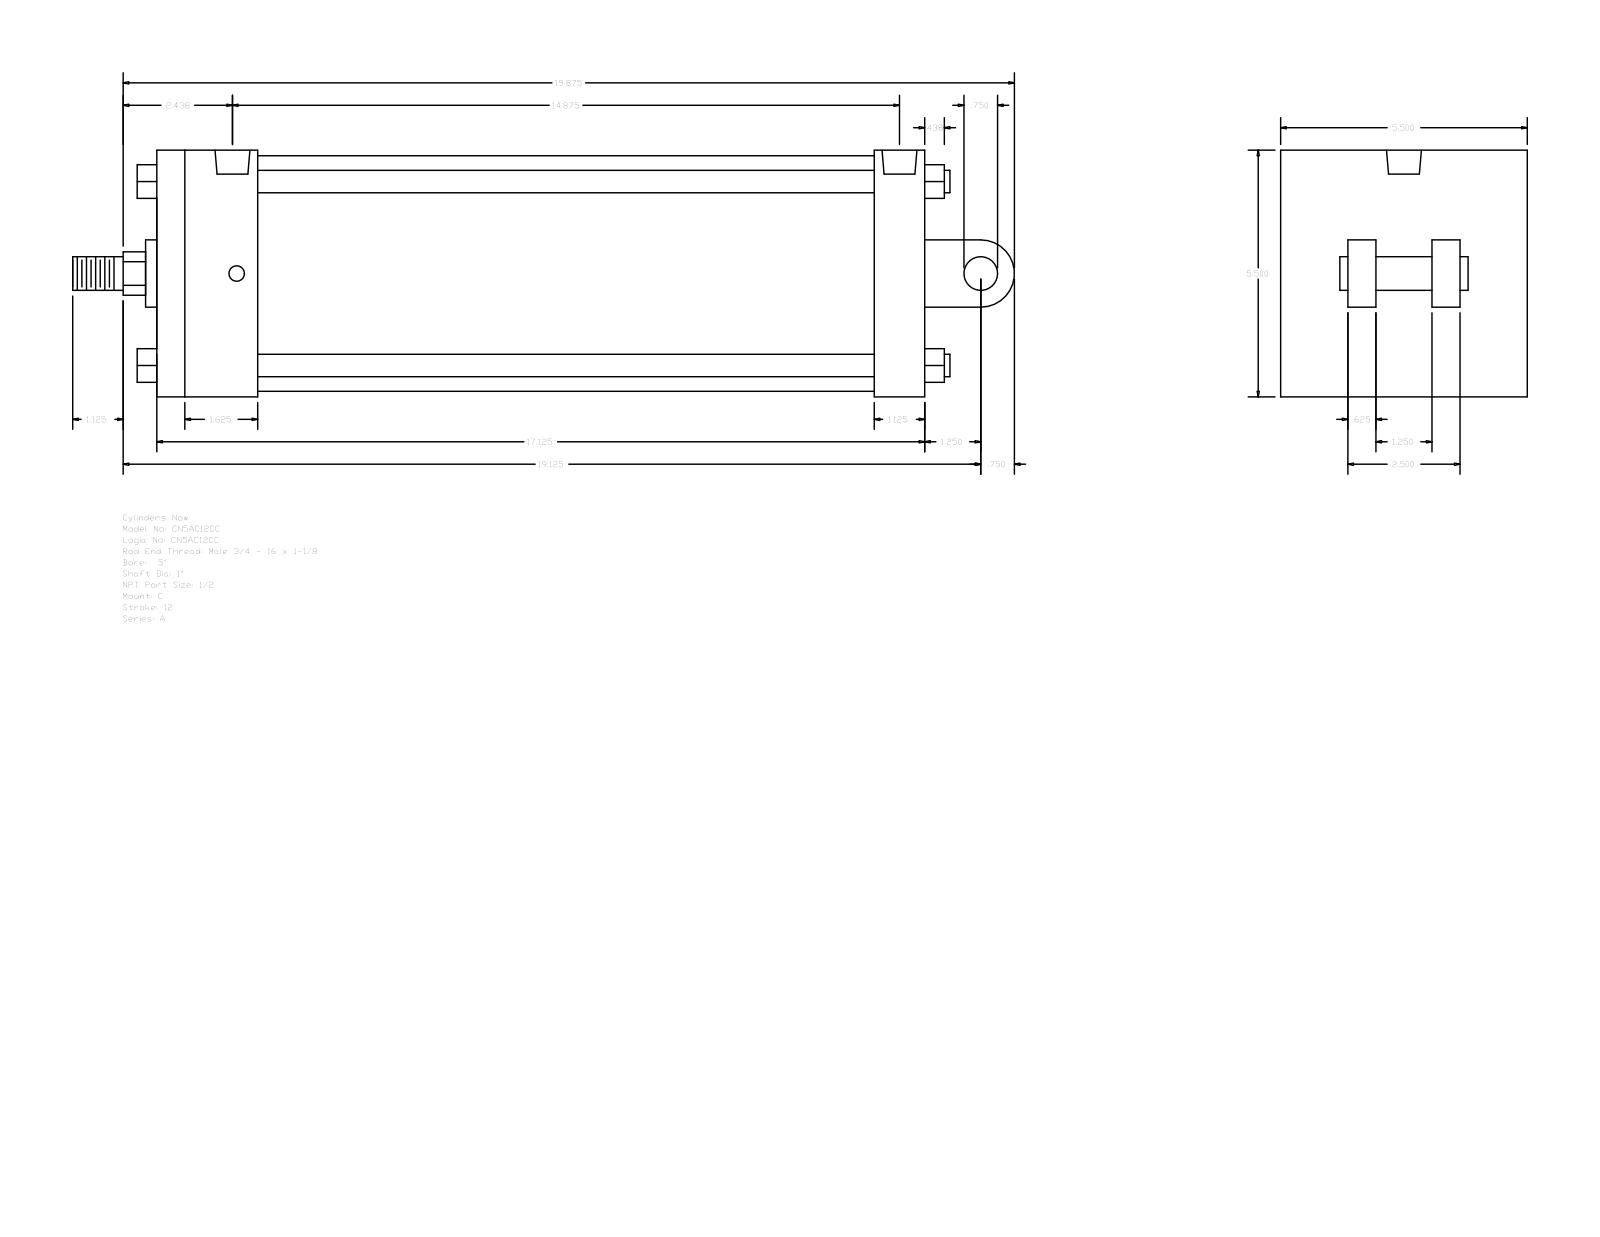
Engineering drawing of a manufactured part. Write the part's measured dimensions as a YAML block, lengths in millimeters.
part_name: "A_C__0500_1"
step_written_by: "GSSL Pune (CONFIG_CONTROL_DESIGN)"
units: millimeters
bodies: {solids: 0, faces: 135, planar: 102, cylindrical: 33, other: 0}
overall_size: [533.4, 139.7, 139.7]
round_holes:
  - {diameter: 8.73, count: 4}
  - {diameter: 19.77, count: 2}
round_bosses_or_shafts:
  - {diameter: 12.7, count: 4}
  - {diameter: 19.05, count: 2}
  - {diameter: 133.35, count: 1}
  - {diameter: 38.1, count: 1}
  - {diameter: 25.4, count: 1}
partial_cylinders:
  - {radius: 12.29, count: 1}
  - {radius: 19.05, count: 1}
face_to_face_distances: [139.7, 434.97, 28.57, 57.15, 406.4, 349.25, 377.82, 38.1, 101.6, 53.97]
hole_center_spacings: [2.39, 373.05, 375.44, 377.83]
